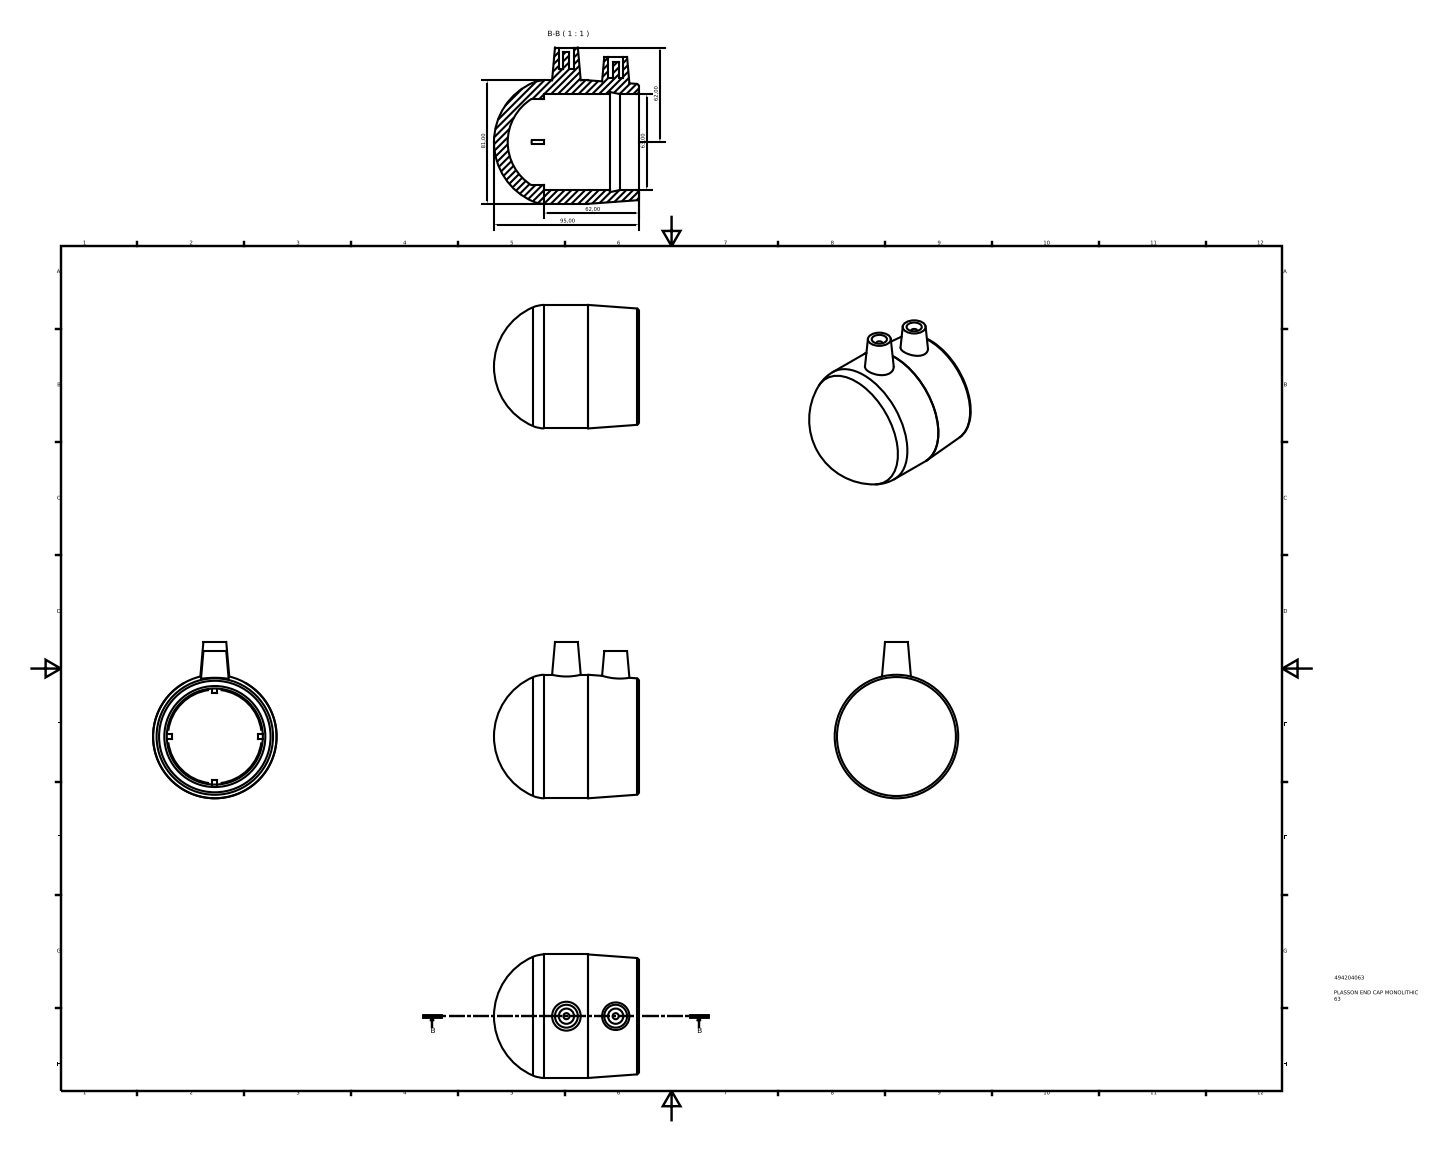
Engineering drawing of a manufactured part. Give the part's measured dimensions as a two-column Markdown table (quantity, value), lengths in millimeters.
| quantity | value |
| --- | --- |
| part name | 494204063 |
| STEP written by | Autodesk Inventor 2015 (AUTOMOTIVE_DESIGN) |
| units | millimeters |
| bodies | 1 solid, 45 faces (24 planar, 7 cylindrical, 14 other) |
| overall size | 102.5 × 95 × 81 |
| volume | 182 972 mm³ |
| surface area | 46 254 mm² |
| round holes (diameter × count) | 10 × 2, 63 × 1 |
| round bosses / shafts (diameter × count) | 4 × 2, 81 × 1 |
| main face-to-face distances | 19, 6.2, 14, 26.78, 29.92, 20.2, 7.8, 56.7, 3.14, 43 |
| hole center spacings | 32.3 |
